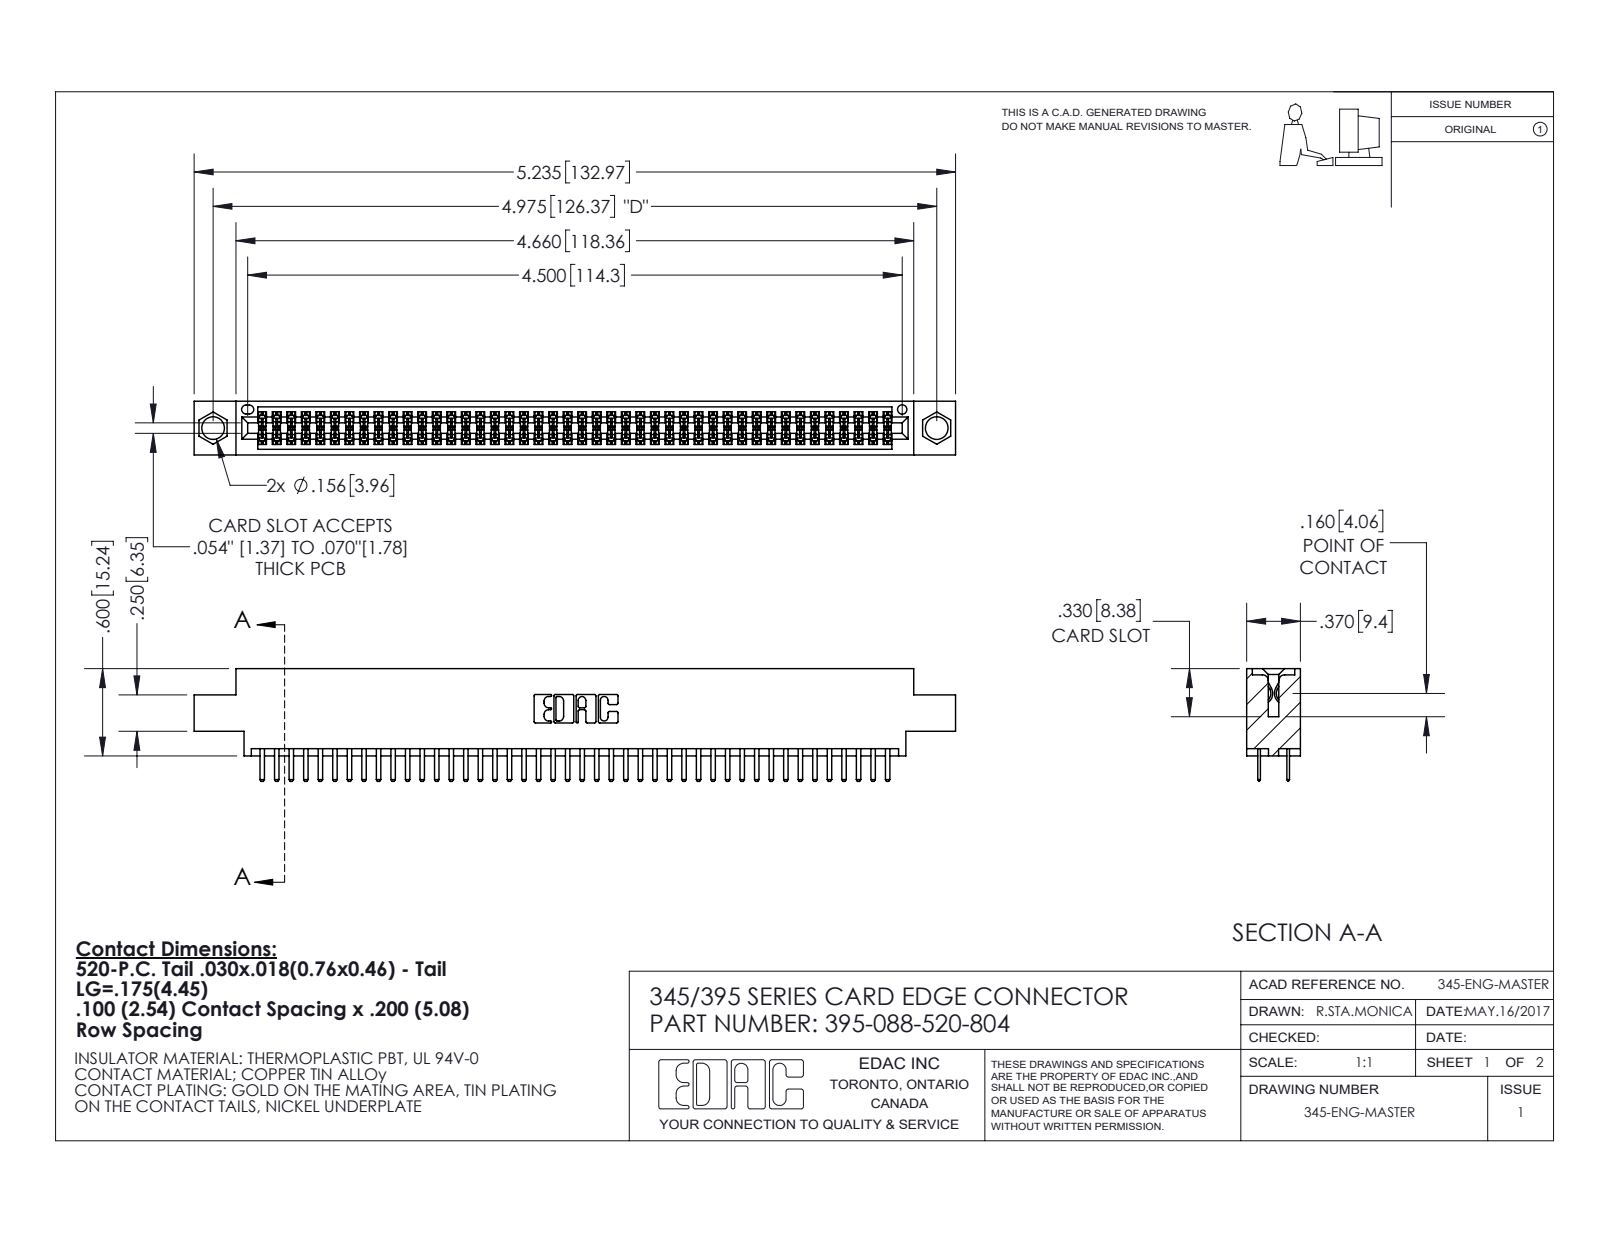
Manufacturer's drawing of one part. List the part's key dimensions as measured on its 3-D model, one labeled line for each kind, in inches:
Part name (STEP PRODUCT): 345-292-001_345-293-120; 345 Part_0.170 Offset - 0.156 Dia-TI; 395-088-520-804
STEP written by: SolidWorks 2020 (CONFIG_CONTROL_DESIGN)
Units: inches
Bodies: 89 solids, 4896 faces (3178 planar, 1718 cylindrical, 0 other)
Overall size (bounding box): 5.235 × 0.775 × 0.37
Volume: 0.774 in³ · Surface area: 28.97 in²
Round holes (diameter × count): ⌀0.156 ×2, ⌀0.064 ×1
Partial cylindrical surfaces — rounded edges, fillets, slot ends (radius × count): R0.006 ×176, R0.01 ×92, R0.01 ×22, R0.007 ×6, R0.031 ×6, R0.026 ×3, R0.014 ×2, R0.019 ×2
Main face-to-face distances: 0.072, 0.298, 0.2, 0.37, 0.098, 0.272, 0.025, 0.225, 0.022, 0.175
Hole centre spacings: 0.27, 4.739, 4.975
